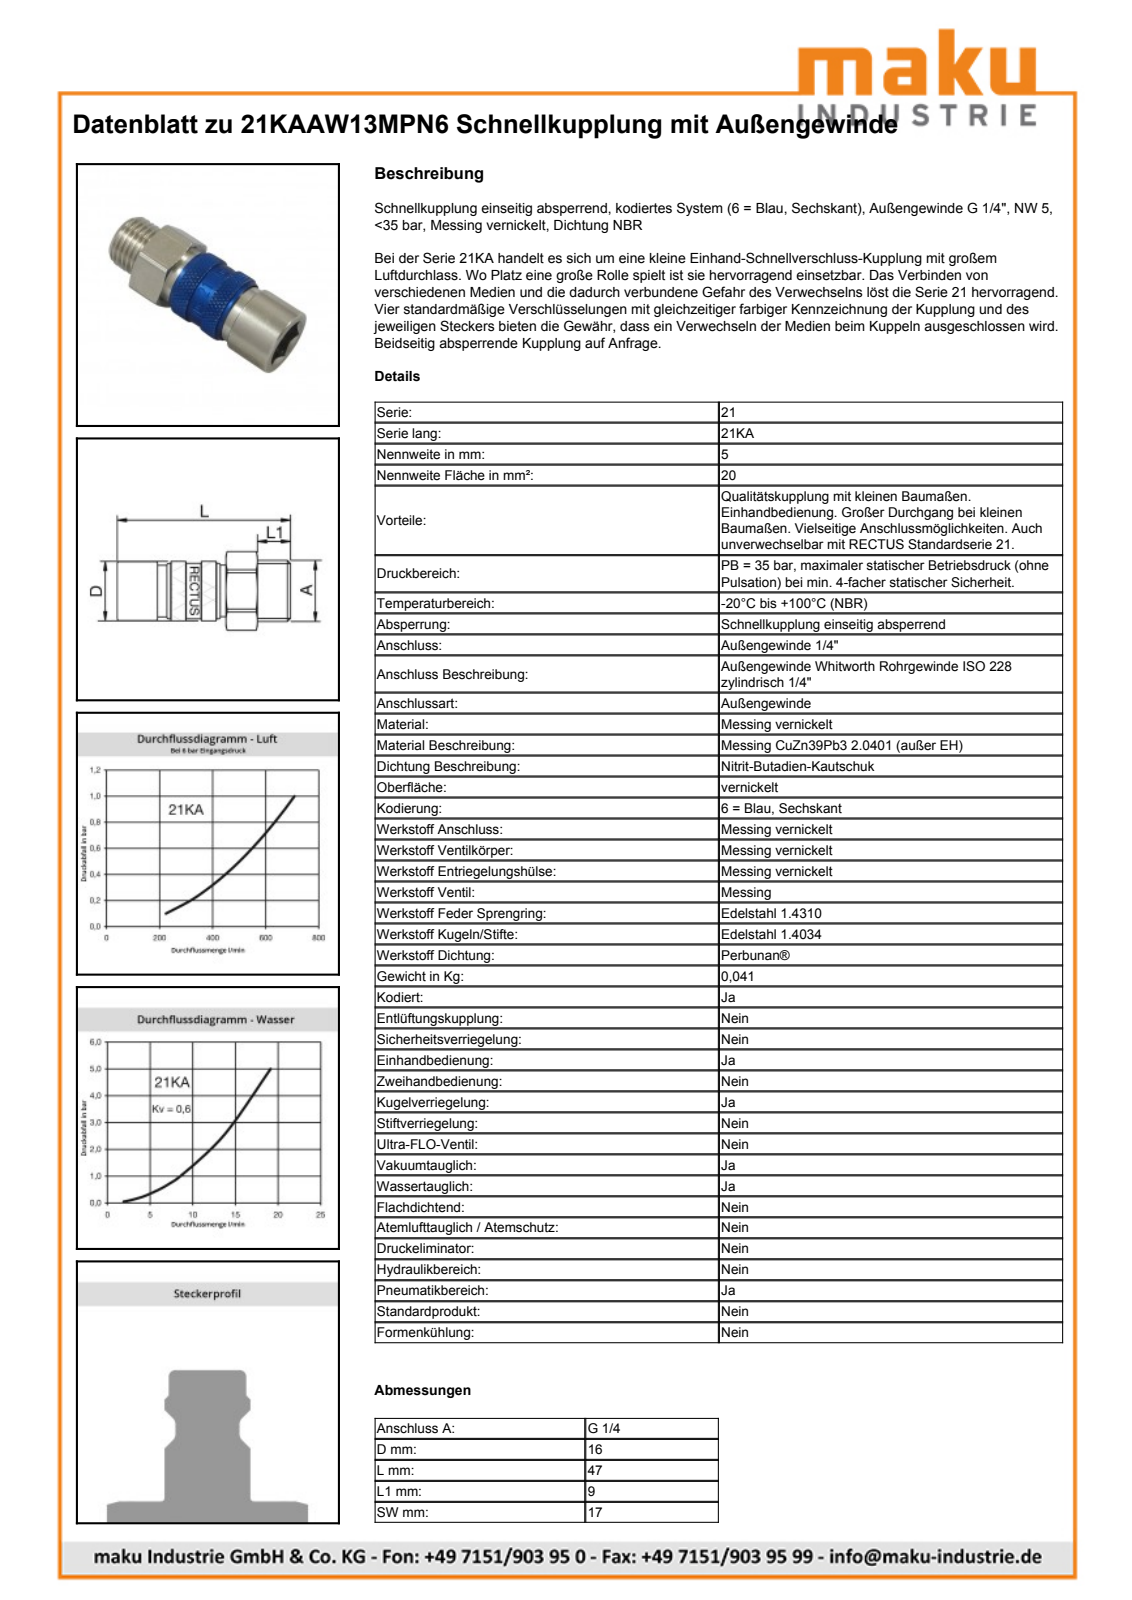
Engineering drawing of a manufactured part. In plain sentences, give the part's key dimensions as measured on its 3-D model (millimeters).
The part is named "D107372". Its 3-D file was written by "Autodesk Inventor 2013 (AUTOMOTIVE_DESIGN)". It is 1 solid with 424 faces: 167 planar, 54 cylindrical and 203 other. Overall it measures 46.99 by 19.02 by 18.2 millimeters. Its volume is 8 019 cubic millimeters and its surface area 3 996 square millimeters. Round holes: 1 of diameter 14. Round bosses or shafts: 1 of diameter 16.15, 1 of diameter 15.8, 1 of diameter 15.1, 1 of diameter 13.16, 1 of diameter 12.89. Partial cylindrical surfaces (rounded edges, fillets, slot ends): 1 of radius 7.45, 1 of radius 9.57. The main face-to-face distances are 17, 10, 38.99, 29.99, 9, 21.44, 8.55, 17.55, 8, 29.44.
